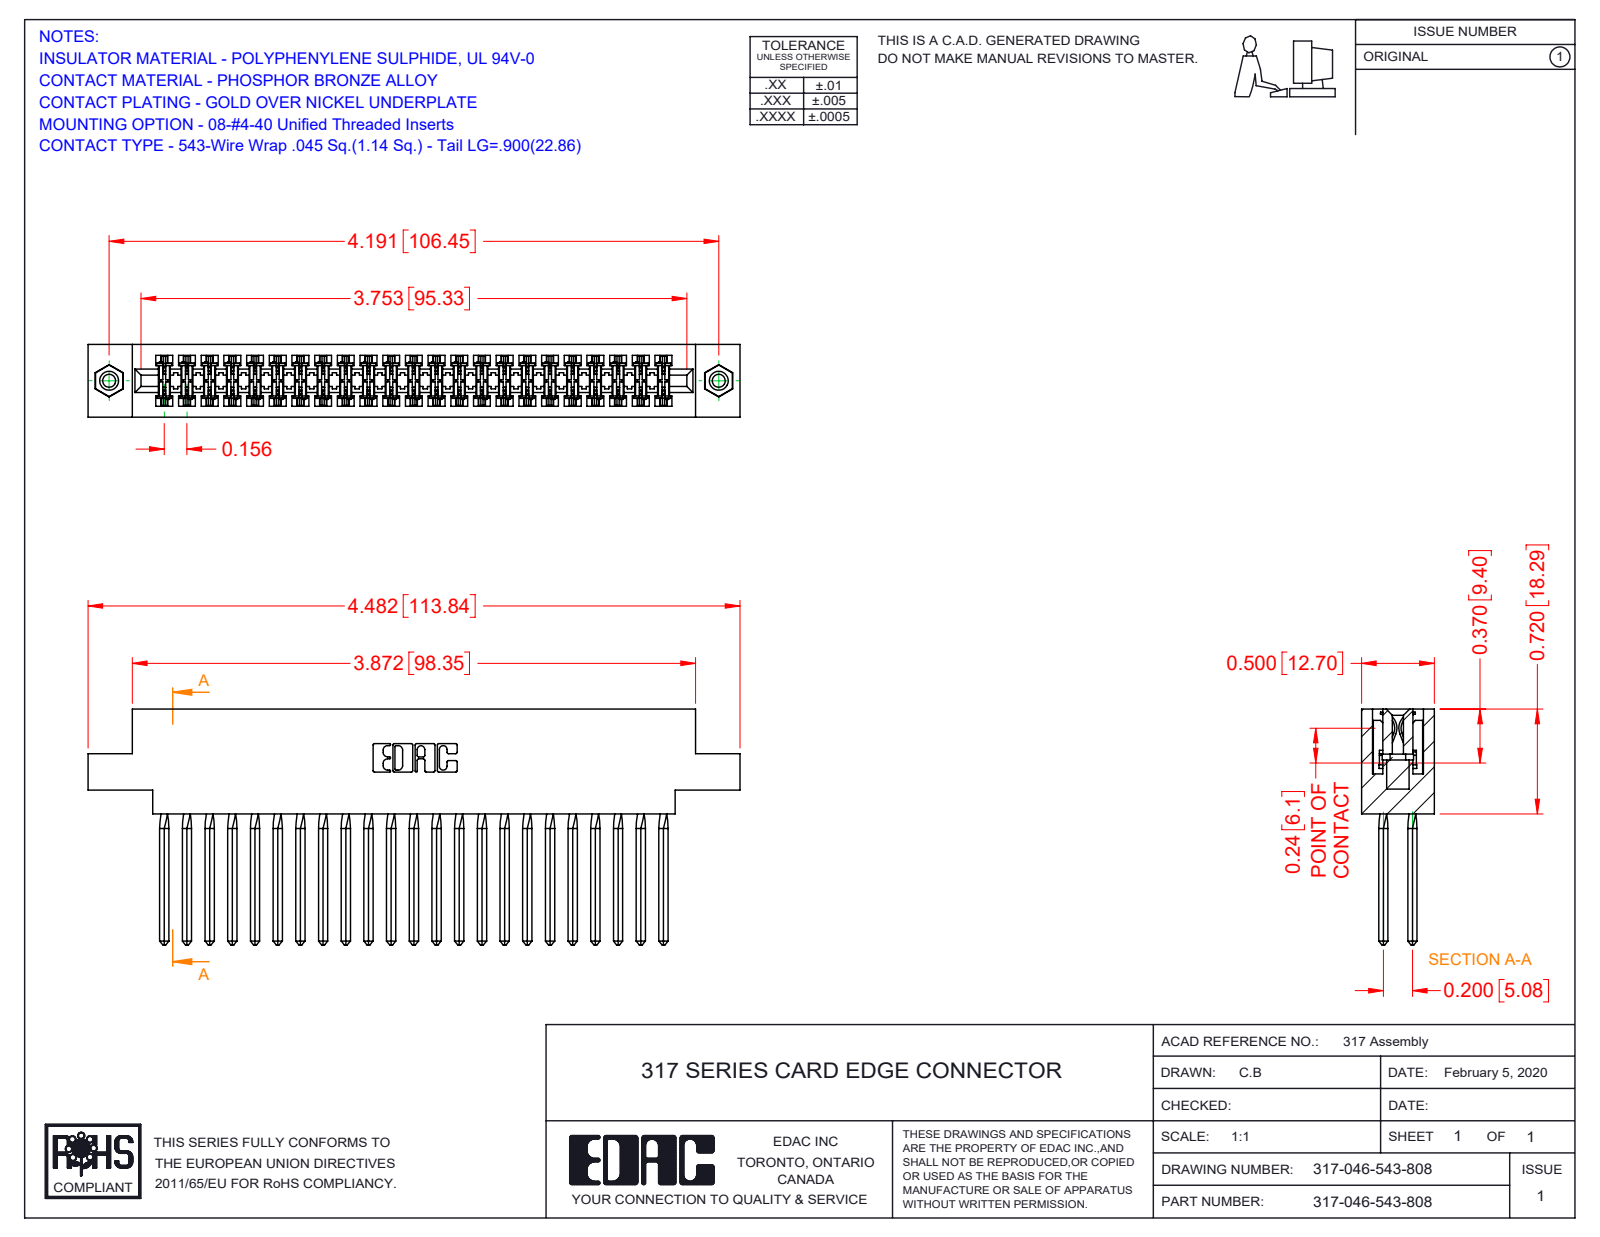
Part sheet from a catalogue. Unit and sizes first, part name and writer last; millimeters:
Units: millimetres
Overall size (bounding box): 113.8 × 41.1 × 12.7
Round holes (diameter × count): ⌀2.3 ×2, ⌀3.2 ×2, ⌀4 ×2
Round bosses / shafts (diameter × count): ⌀3.9 ×2
Partial cylindrical surfaces — rounded edges, fillets, slot ends (radius × count): R0.4 ×92, R0.3 ×22, R0.2 ×6, R0.8 ×6, R0.7 ×3, R2.4 ×2, R2.5 ×2, R2.8 ×2
Main face-to-face distances: 12.7, 1.9, 10.8, 2.8, 8.9, 5, 5.6, 2.4, 18.3, 5.1
Hole centre spacings: 106.5
Volume: 18 680 mm³ · Surface area: 27 630 mm²
Bodies: 49 solids, 4256 faces (3448 planar, 608 cylindrical, 200 other)
Part name (STEP PRODUCT): 345-250-001_345-250-003-102; 317-290-001_543; 317 Part_.156 Dia - TI; 317-046-543-878
STEP written by: SolidWorks 2016 (CONFIG_CONTROL_DESIGN)
